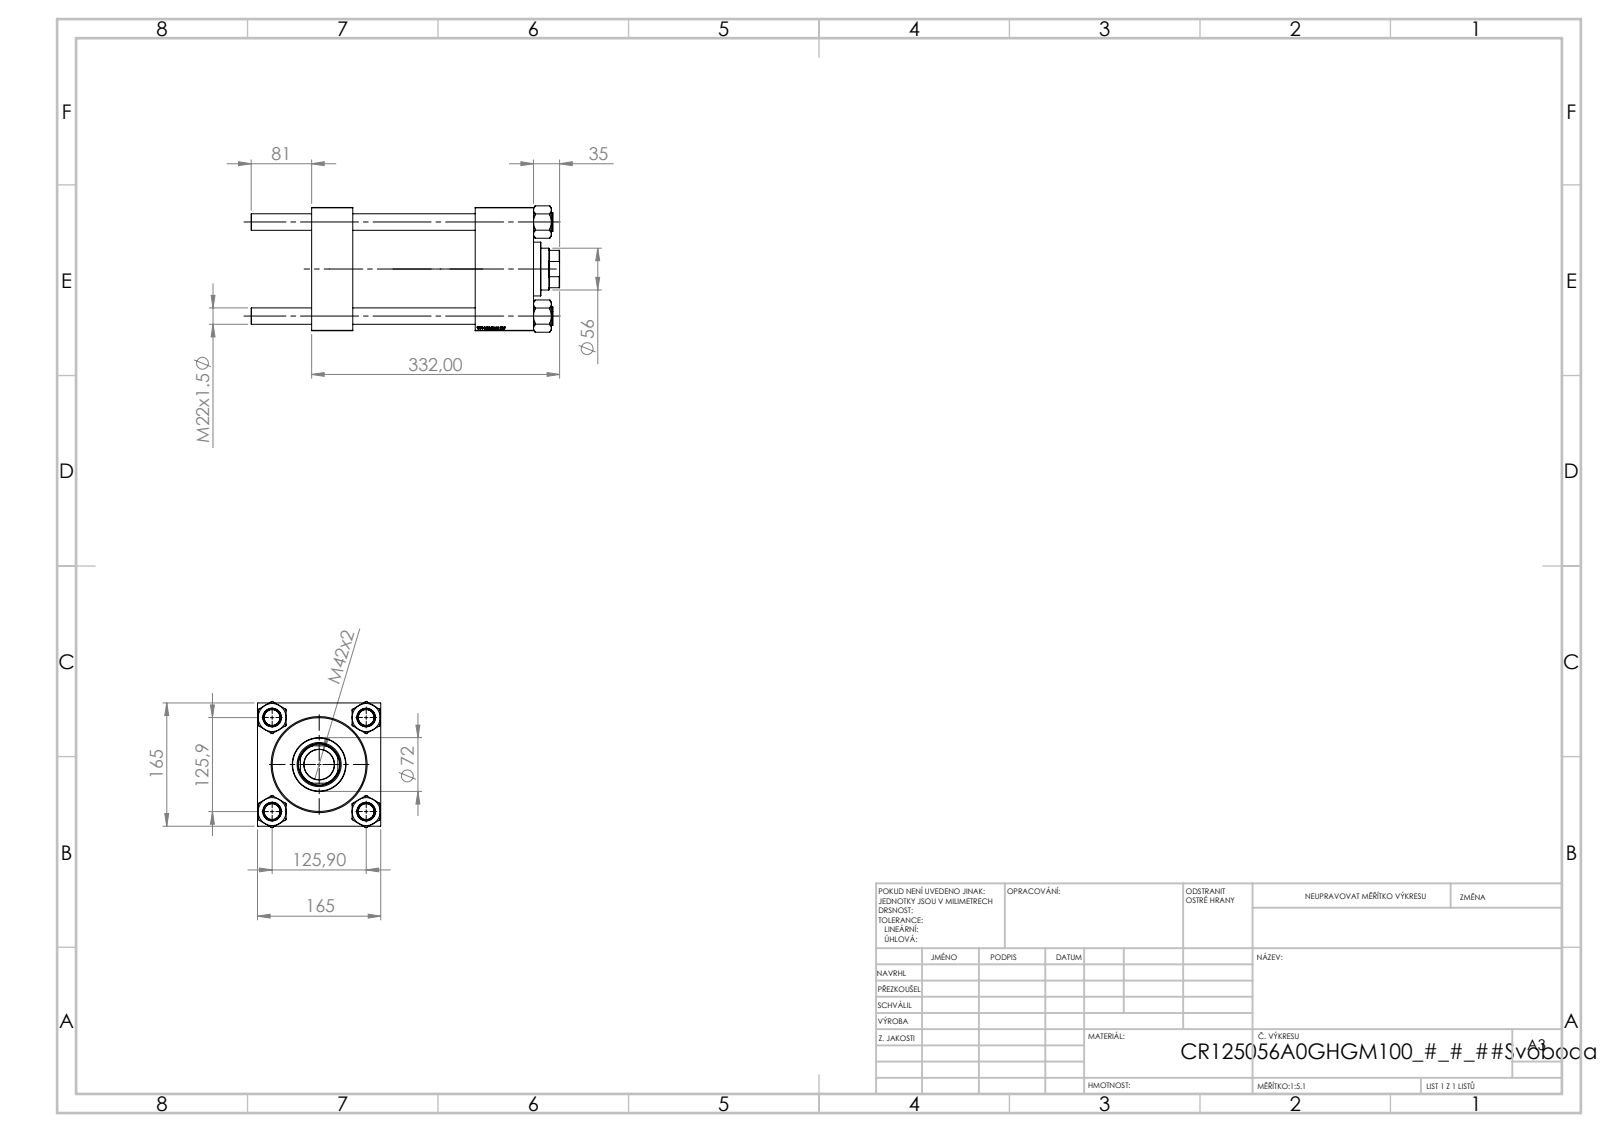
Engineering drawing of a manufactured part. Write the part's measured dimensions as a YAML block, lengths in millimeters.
part_name: "V215_VC_A; NUT_M5; CR025_012_A_0_G_A_G_M_020_+#_##_TYCINKA; V215CR_VCP (+1 more)"
step_written_by: "SolidWorks 2019 (CONFIG_CONTROL_DESIGN)"
units: millimeters
bodies: {solids: 11, faces: 1182, planar: 568, cylindrical: 78, other: 536}
overall_size: [413, 169.14, 165]
volume: 5096000
surface_area: 649179
round_holes:
  - {diameter: 22, count: 4}
  - {diameter: 7, count: 2}
  - {diameter: 32.24, count: 2}
  - {diameter: 45, count: 2}
  - {diameter: 40.5, count: 1}
  - {diameter: 56, count: 1}
  - {diameter: 59, count: 1}
  - {diameter: 96, count: 1}
  - {diameter: 125, count: 1}
  - {diameter: 125.5, count: 1}
round_bosses_or_shafts:
  - {diameter: 25, count: 4}
  - {diameter: 131, count: 1}
  - {diameter: 72, count: 1}
partial_cylinders:
  - {radius: 27, count: 1}
face_to_face_distances: [165, 55, 297, 242, 219, 164, 78, 268.3, 213.3, 49.3]
hole_center_spacings: [89.02, 125.9, 178.05, 218.5]
